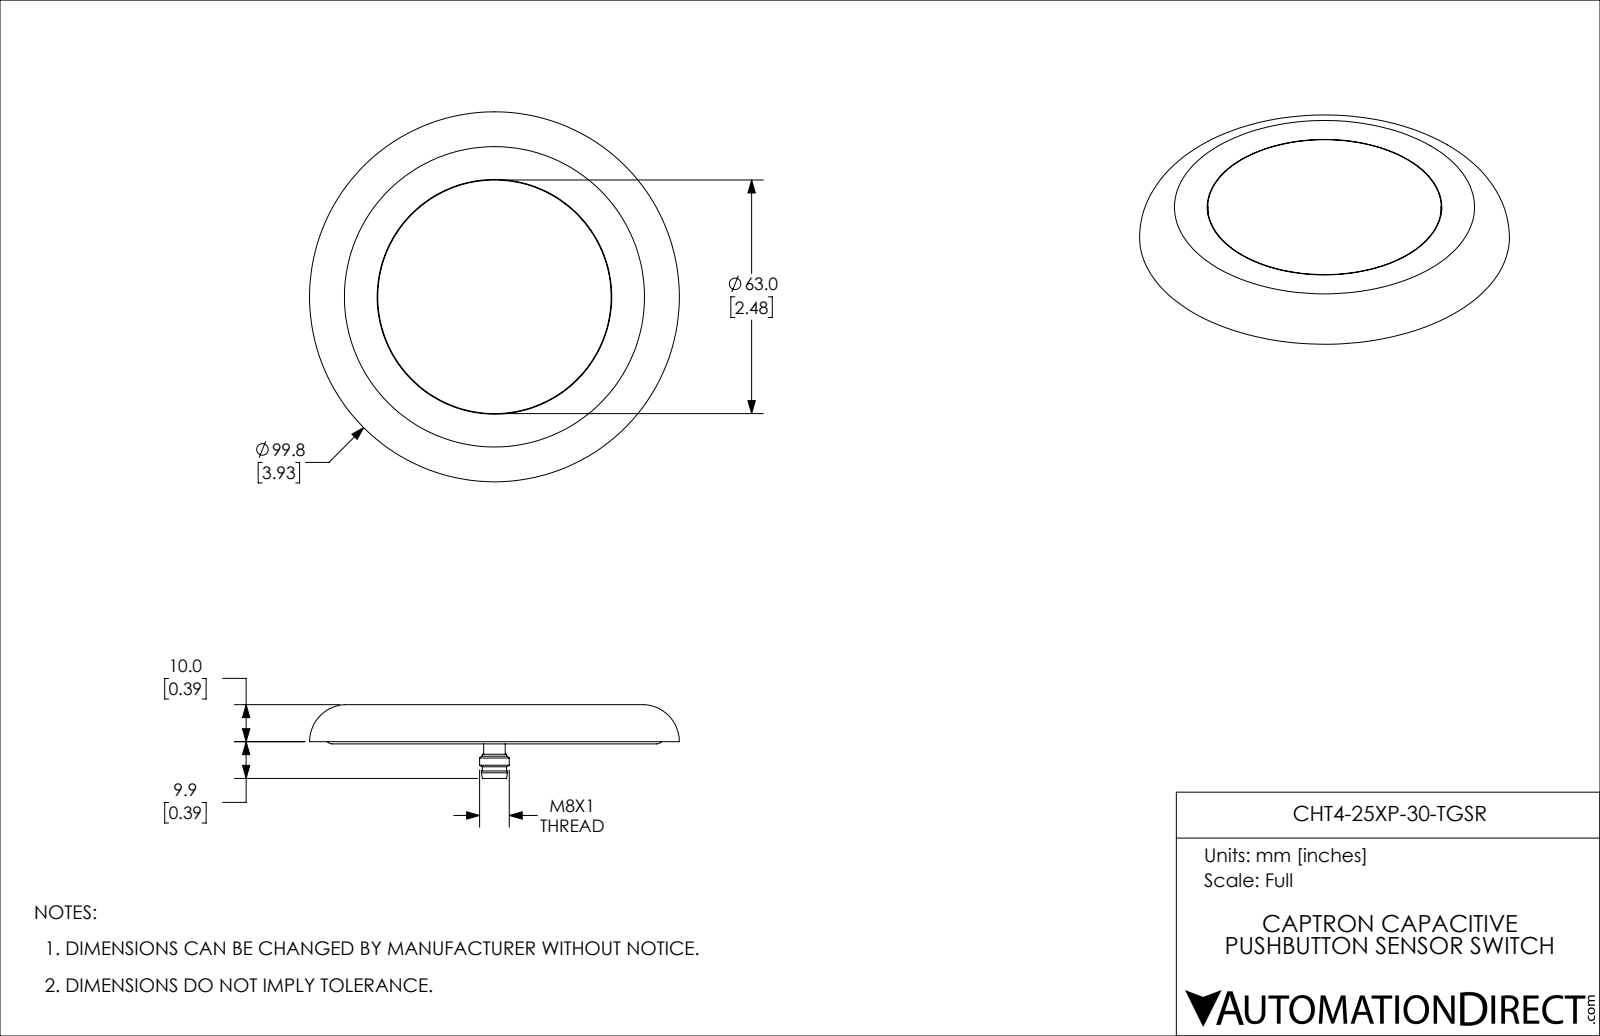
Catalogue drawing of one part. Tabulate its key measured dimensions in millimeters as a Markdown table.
| quantity | value |
| --- | --- |
| part name | CHT4-25XP-30-TGSR |
| STEP written by | SolidWorks 2019 (CONFIG_CONTROL_DESIGN) |
| units | millimeters |
| bodies | 13 solids, 102 faces (30 planar, 32 cylindrical, 40 other) |
| overall size | 99.8 × 99.8 × 19.9 |
| volume | 28 699 mm³ |
| surface area | 41 184 mm² |
| round holes (diameter × count) | 6 × 1, 58.4 × 1, 63.31 × 1, 64.6 × 1 |
| round bosses / shafts (diameter × count) | 1 × 4, 63 × 1, 8 × 1, 7 × 1, 6.5 × 1, 5.8 × 1 |
| partial cylindrical surfaces (radius × count) | 32 × 1 |
| main face-to-face distances | 8.28, 1.42, 9.7, 1.45, 8.24, 6.82, 1.46, 9.9, 1.62, 8.44 |
| hole center spacings | 3.19 |
